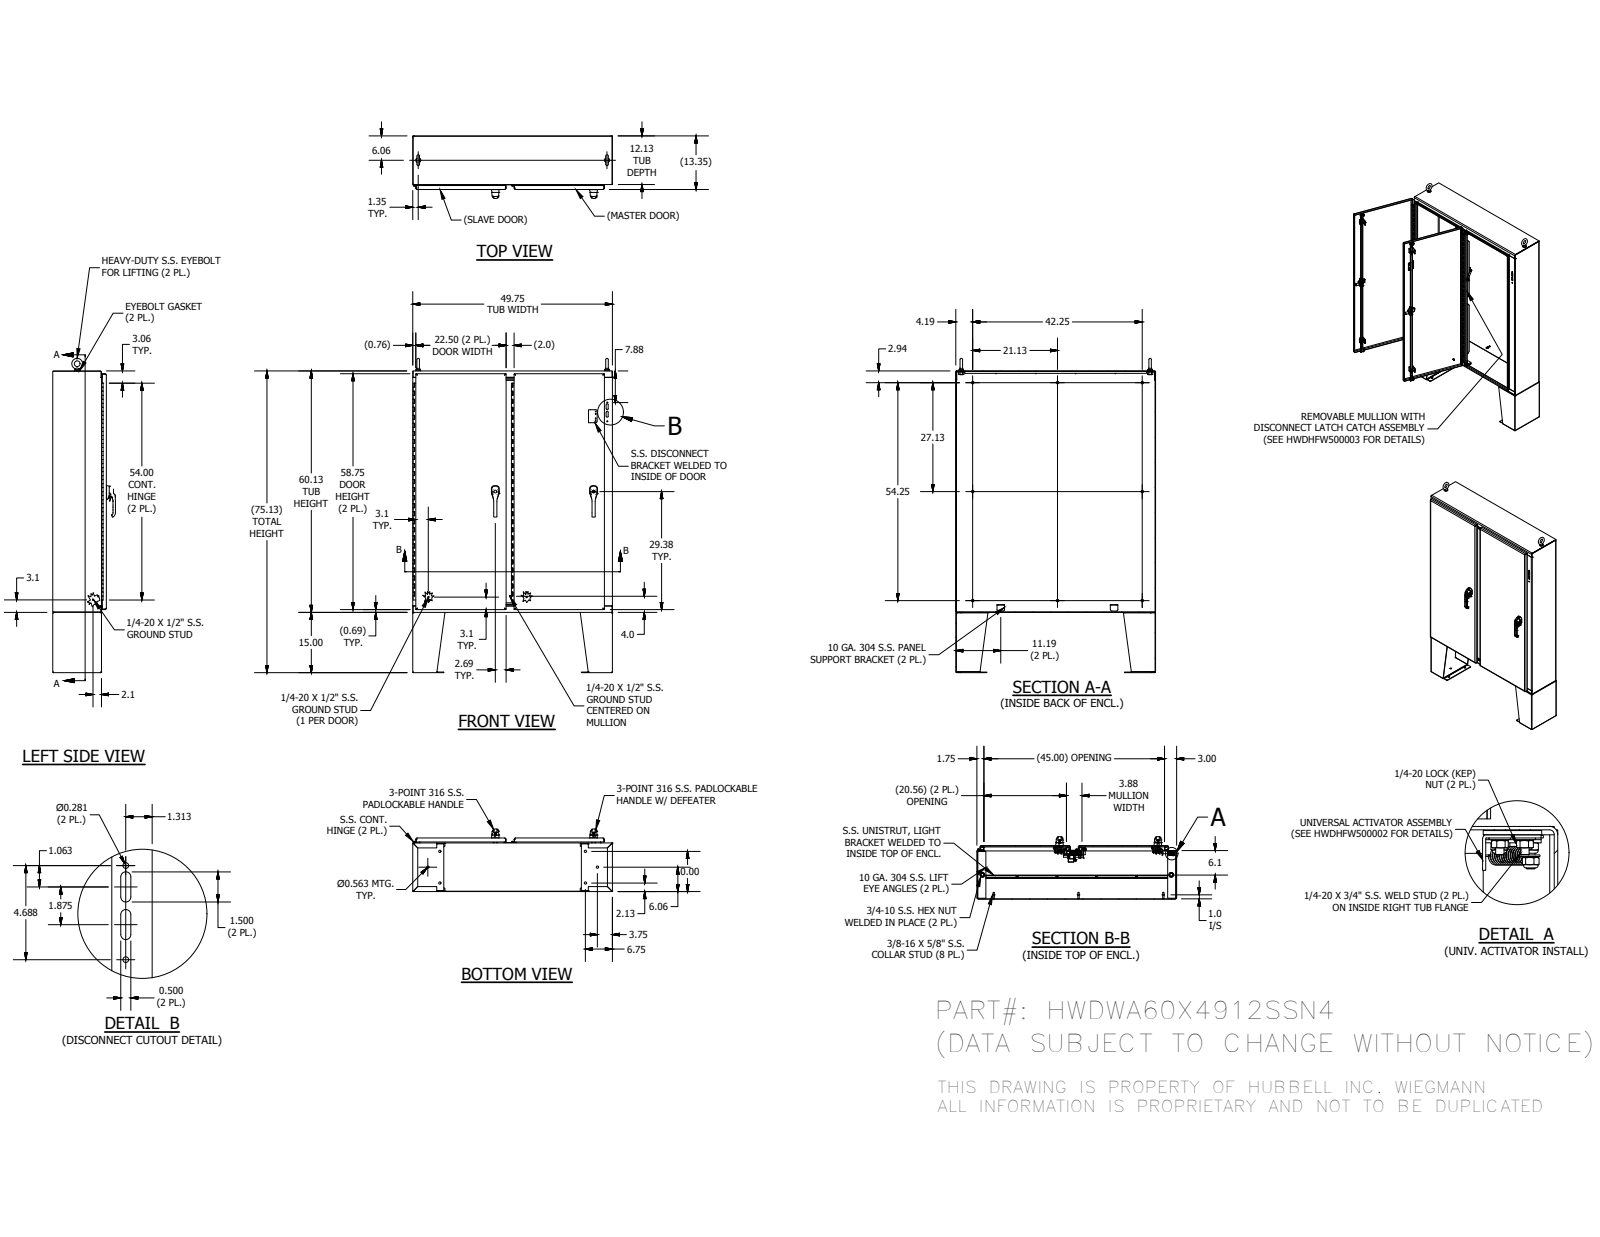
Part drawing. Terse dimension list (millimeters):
name: WA60X4912SSN4BLR; WAX4912SSN4TOP; WAX4912SSN4BTM; HFW332010S (+8 more)
written by: Autodesk Inventor 2016 (AUTOMOTIVE_DESIGN)
unit: mm
bodies: 217 solids, 8968 faces (4124 planar, 3044 cylindrical, 1800 other)
size: 1987.49 × 1263.65 × 396.15
volume: 20 480 000 mm³; area: 15 450 000 mm²
holes: 18× ⌀6.35, 18× ⌀9.52, 18× ⌀14.29, 10× ⌀4.98, 9× ⌀4.76, 8× ⌀4.83, 8× ⌀6.65, 8× ⌀7.14, 8× ⌀7.33, 8× ⌀8.51, 8× ⌀9.65, 6× ⌀3.96
bosses: 21× ⌀6.35, 18× ⌀8.38, 13× ⌀15.88, 12× ⌀8.56, 11× ⌀9.52, 9× ⌀14.29, 8× ⌀7.11, 6× ⌀25.4
rounds: 359× R0.5, 221× R0.3, 192× R0.51, 55× R3.17, 42× R0.47, 28× R1.27, 28× R2, 23× R6.35
face distances: 2.64, 336.39, 333.75, 339.03, 1261, 305.33, 31.06, 1524.54, 3.17, 302.69
hole spacings: 621.87, 9.65, 19.31, 30.36, 37.06, 51.83, 88.97, 126.05
